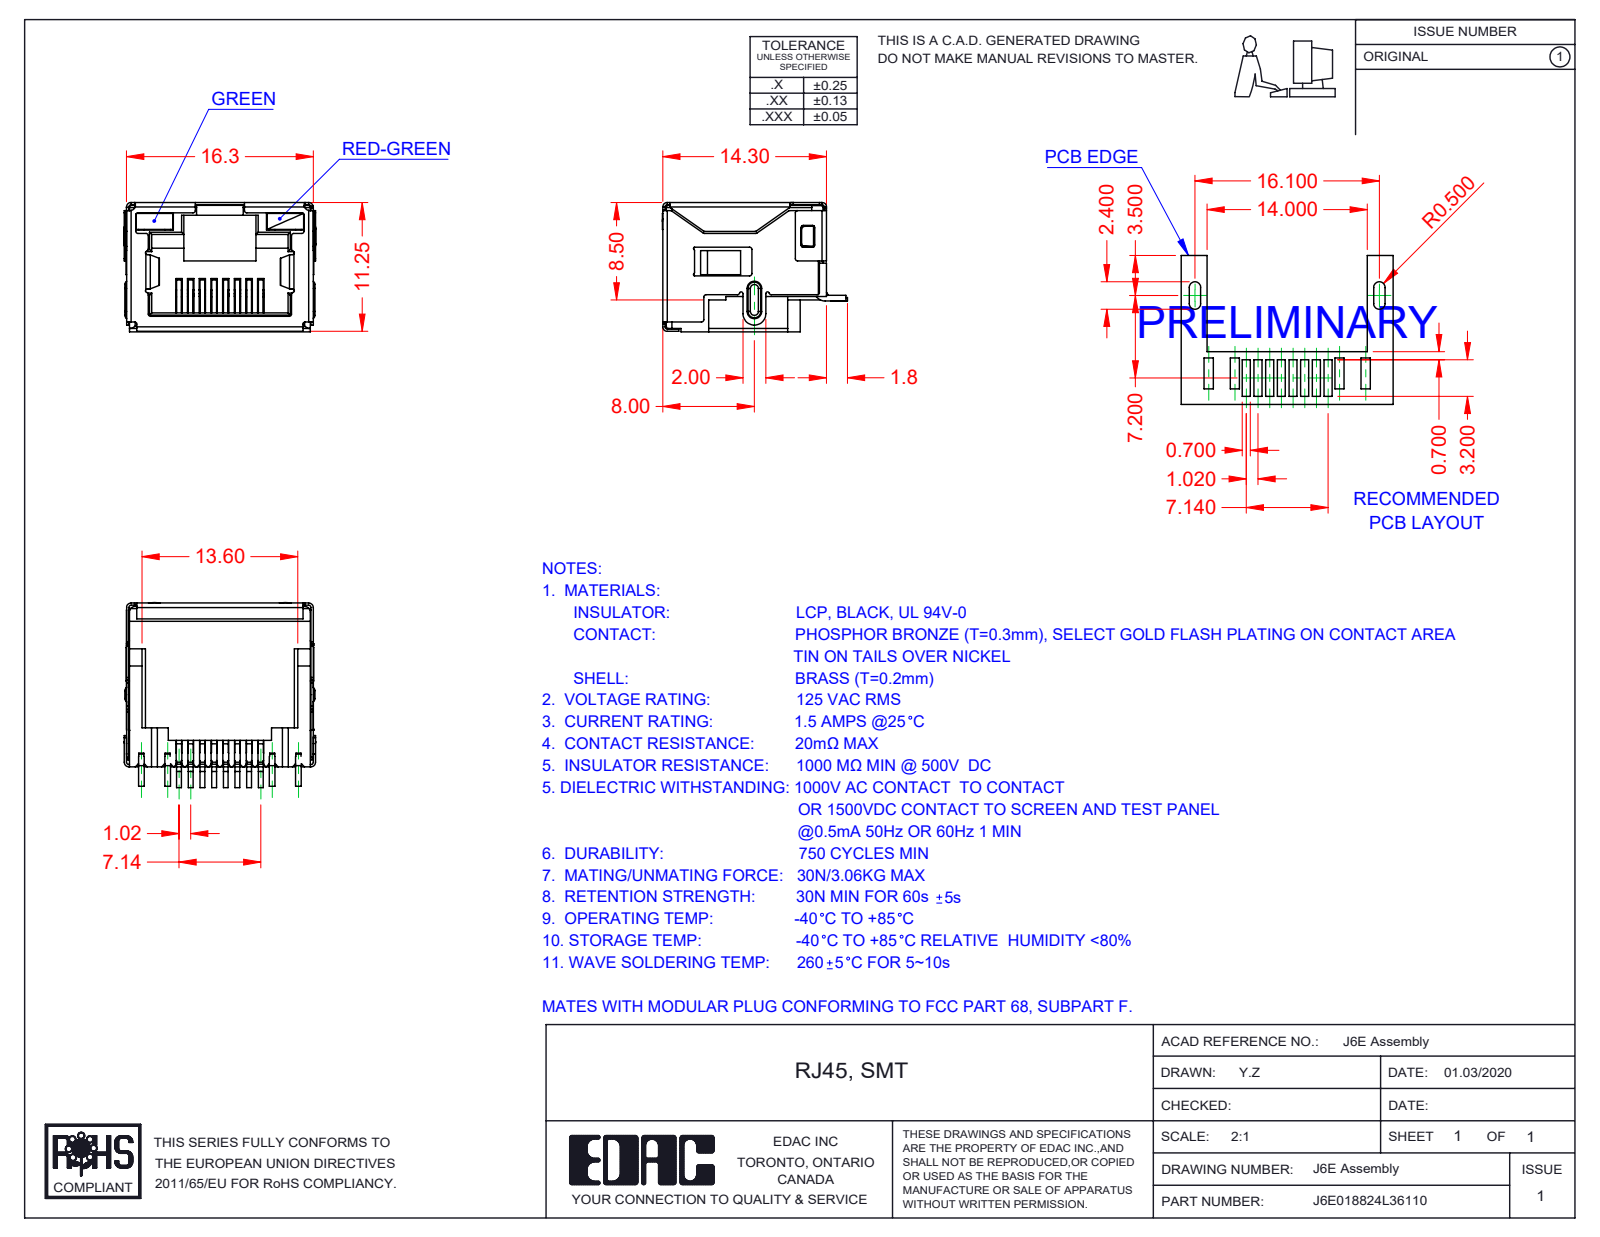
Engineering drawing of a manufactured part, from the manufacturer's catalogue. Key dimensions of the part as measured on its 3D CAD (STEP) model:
Part name (STEP PRODUCT): 6E Shield_LED; 6E Contacts; 6E Insulator_LED; J6E018824L36110 (+2 more)
STEP written by: SolidWorks 2016 (CONFIG_CONTROL_DESIGN)
Units: millimetres
Bodies: 12 solids, 1498 faces (1099 planar, 349 cylindrical, 50 other)
Overall size (bounding box): 16.75 × 16.15 × 11.3
Volume: 1 109 mm³ · Surface area: 4 045 mm²
Partial cylindrical surfaces — rounded edges, fillets, slot ends (radius × count): R0.2 ×82, R0.25 ×17, R0.4 ×13, R0.5 ×13, R0.1 ×10, R0.15 ×7, R0.3 ×4, R1 ×3
Main face-to-face distances: 11.05, 16.05, 16.1, 15.85, 11.1, 11.3, 2.4, 0.7, 9.85, 0.49
